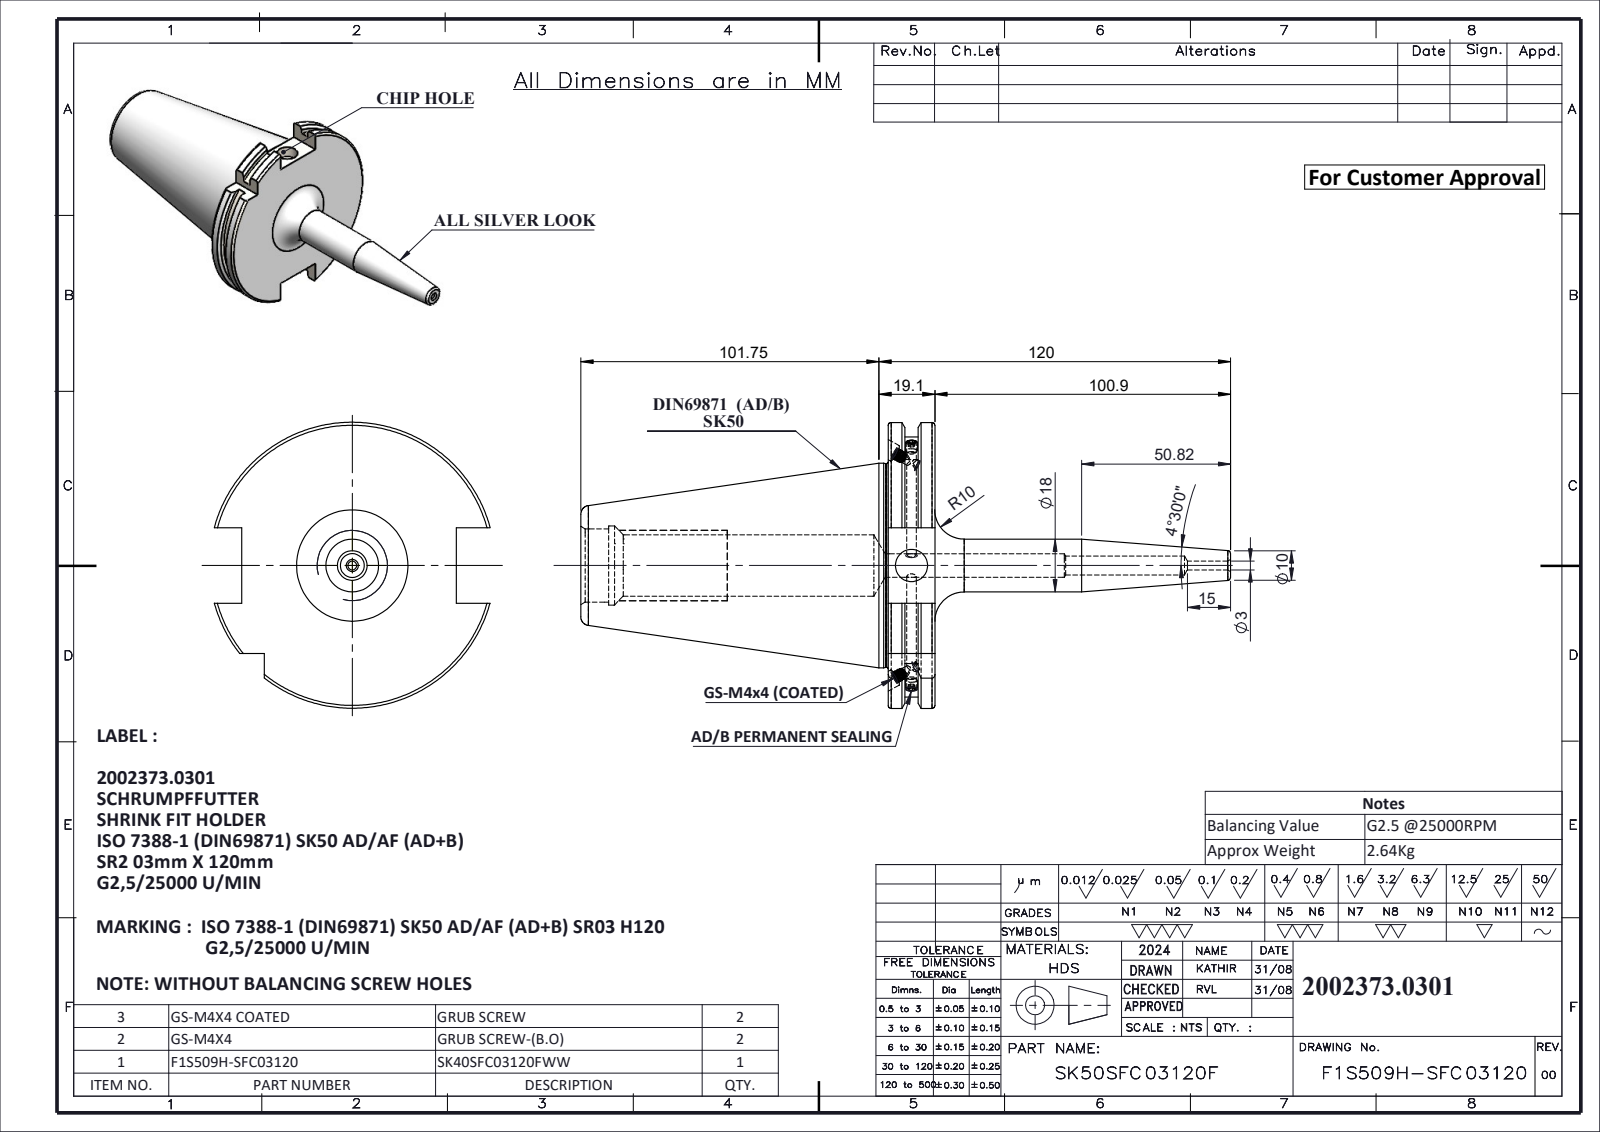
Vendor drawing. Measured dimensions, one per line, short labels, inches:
name: F1S509H-SFC03120; SK50SFC03120FWW; GS-M4X4-COATING_DIN 913 - M4 x 4-N; GS-M4X4_DIN 913 - M4 x 4-N
written by: SolidWorks 2024 (CONFIG_CONTROL_DESIGN)
unit: in
bodies: 5 solids, 252 faces (61 planar, 75 cylindrical, 116 other)
size: 8.73 × 3.839 × 3.703
volume: 20.88 in³; area: 80.29 in²
holes: 2× ⌀0.126, 2× ⌀0.236, 1× ⌀0.118, 1× ⌀0.13, 1× ⌀0.256, 1× ⌀0.315, 1× ⌀0.433, 1× ⌀0.827, 1× ⌀0.984, 1× ⌀1.063
bosses: 4× ⌀0.157, 2× ⌀0.114, 1× ⌀2.75, 1× ⌀2.734, 1× ⌀0.709
rounds: 1× R1.768, 1× R1.919
face distances: 0.626, 0.222, 0.404, 0.399, 0.177, 0.227, 4.132, 4.354, 4.531, 4.758
